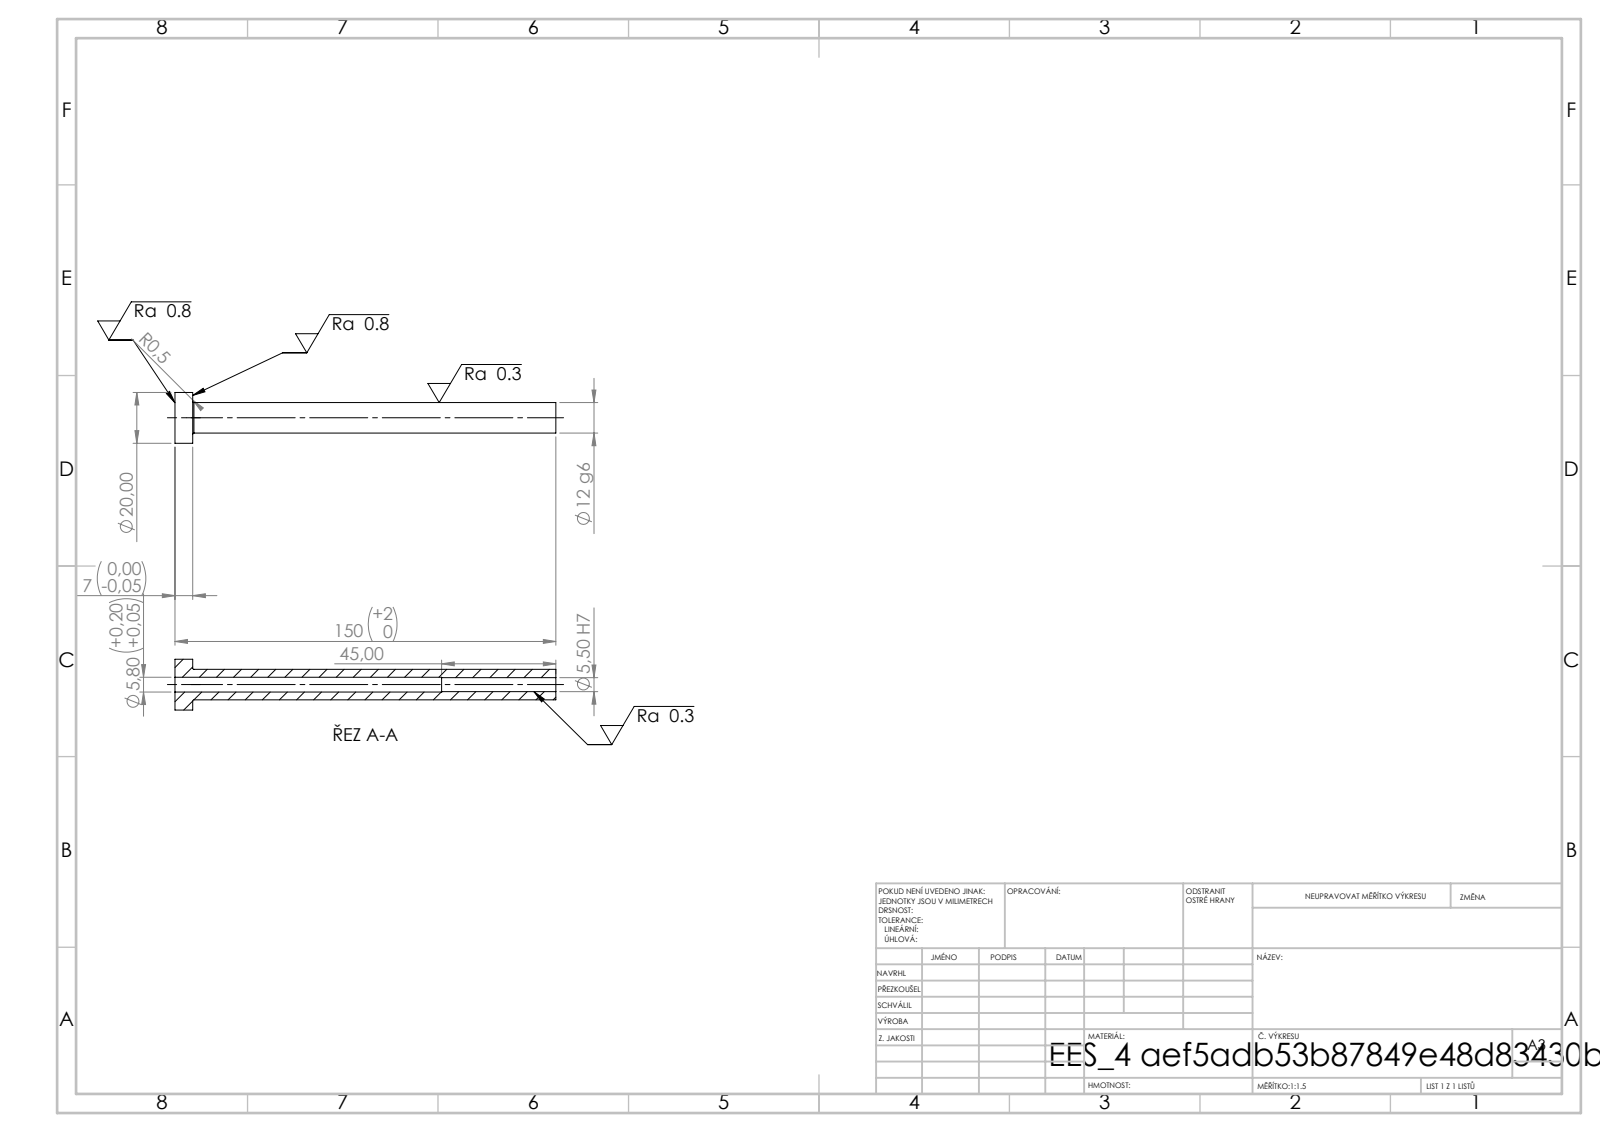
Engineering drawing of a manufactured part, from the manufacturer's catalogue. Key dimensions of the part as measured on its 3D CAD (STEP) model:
STEP written by: SolidWorks 2019 (CONFIG_CONTROL_DESIGN)
Units: millimetres
Bodies: 1 solid, 14 faces (4 planar, 8 cylindrical, 2 other)
Overall size (bounding box): 150 × 20 × 20
Volume: 14 531 mm³ · Surface area: 9 094 mm²
Round holes (diameter × count): ⌀5.5 ×1, ⌀5.8 ×1
Round bosses / shafts (diameter × count): ⌀20 ×1, ⌀12 ×1
Main face-to-face distances: 7, 150, 143, 105, 98, 45
